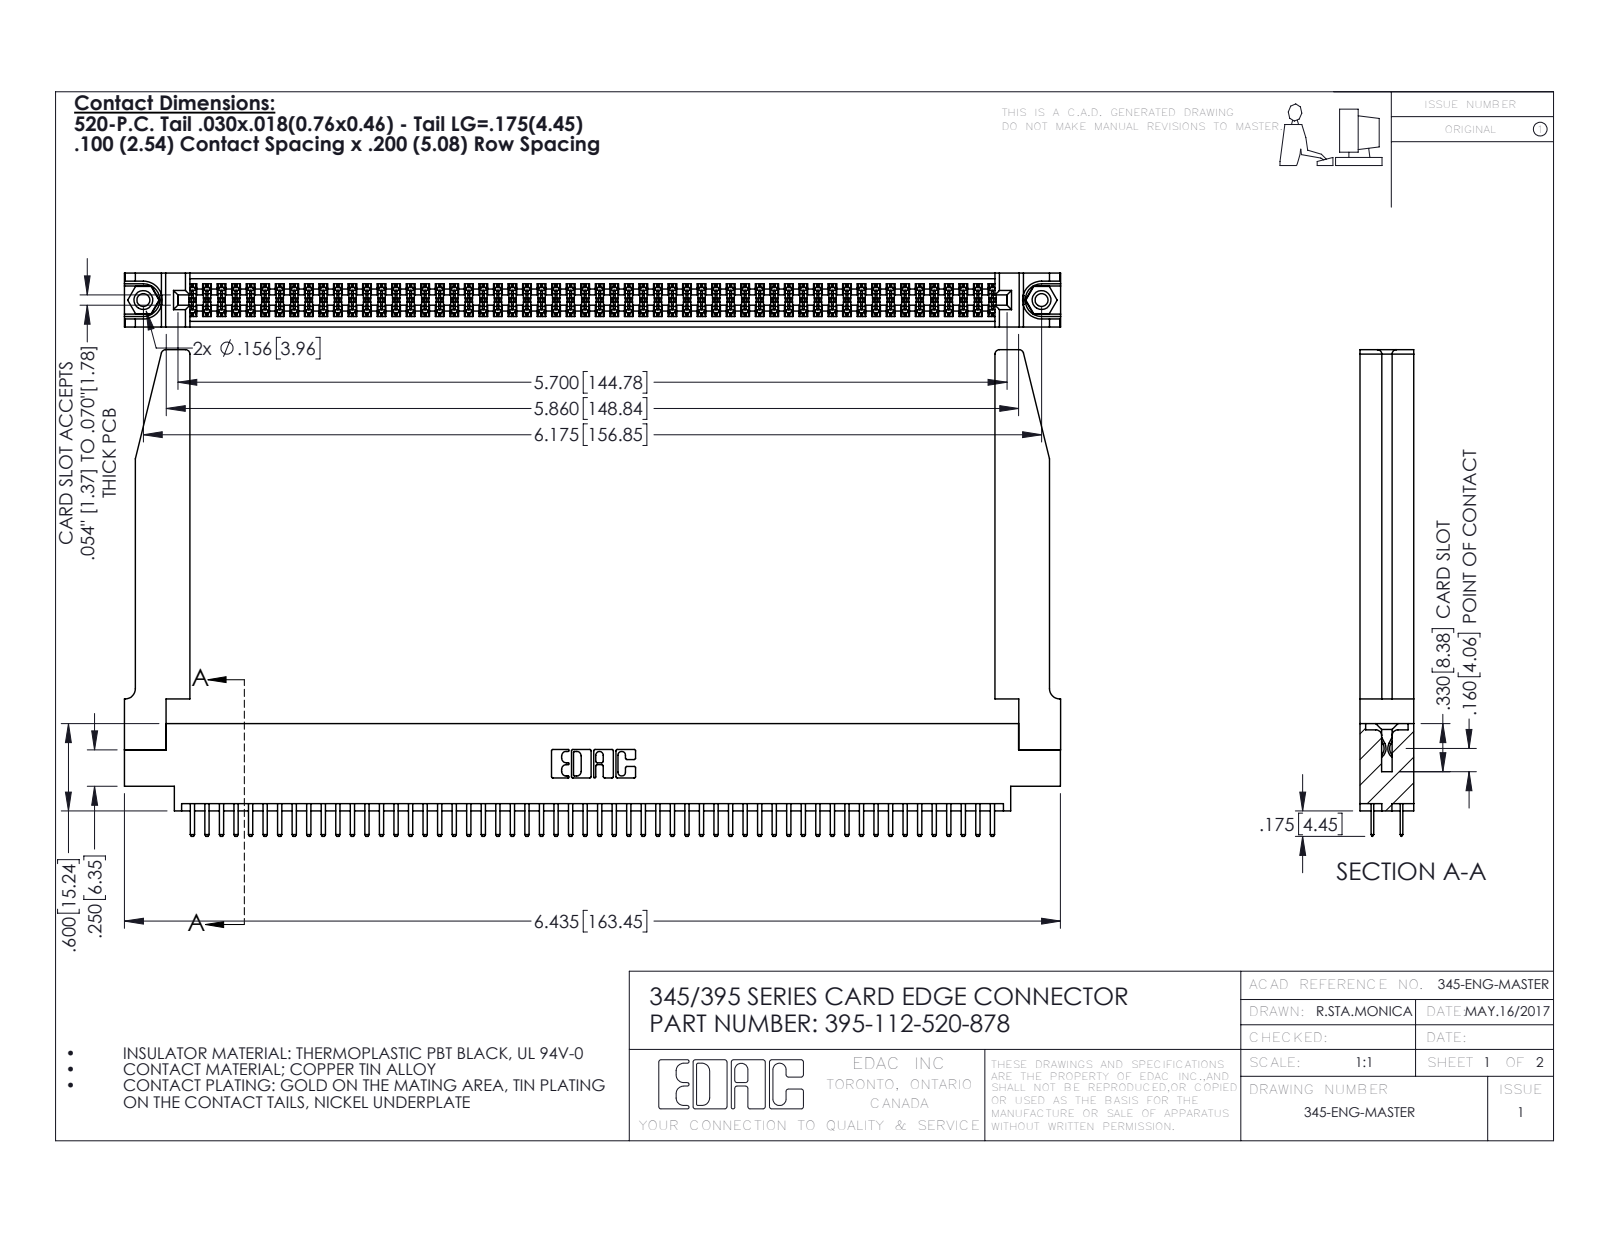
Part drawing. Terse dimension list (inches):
name: 395-112-520-878; 345-220-078_345-220-078; 345 Part_0.170 Offset - 0.156 Dia-TH; 345-292-001_345-293-120 (+1 more)
written by: SolidWorks 2016 (CONFIG_CONTROL_DESIGN)
unit: in
bodies: 117 solids, 6412 faces (4146 planar, 2214 cylindrical, 52 other)
size: 6.436 × 3.345 × 0.37
volume: 1.441 in³; area: 47.39 in²
holes: 2× ⌀0.089, 2× ⌀0.125, 2× ⌀0.156, 1× ⌀0.064
bosses: 2× ⌀0.155
rounds: 168× R0.006, 116× R0.01, 22× R0.01, 8× R0.03, 6× R0.007, 6× R0.031, 3× R0.026, 2× R0.014
face distances: 0.37, 0.072, 0.298, 0.2, 0.098, 0.272, 0.025, 0.225, 0.022, 0.072
hole spacings: 0.27, 5.939, 6.175
